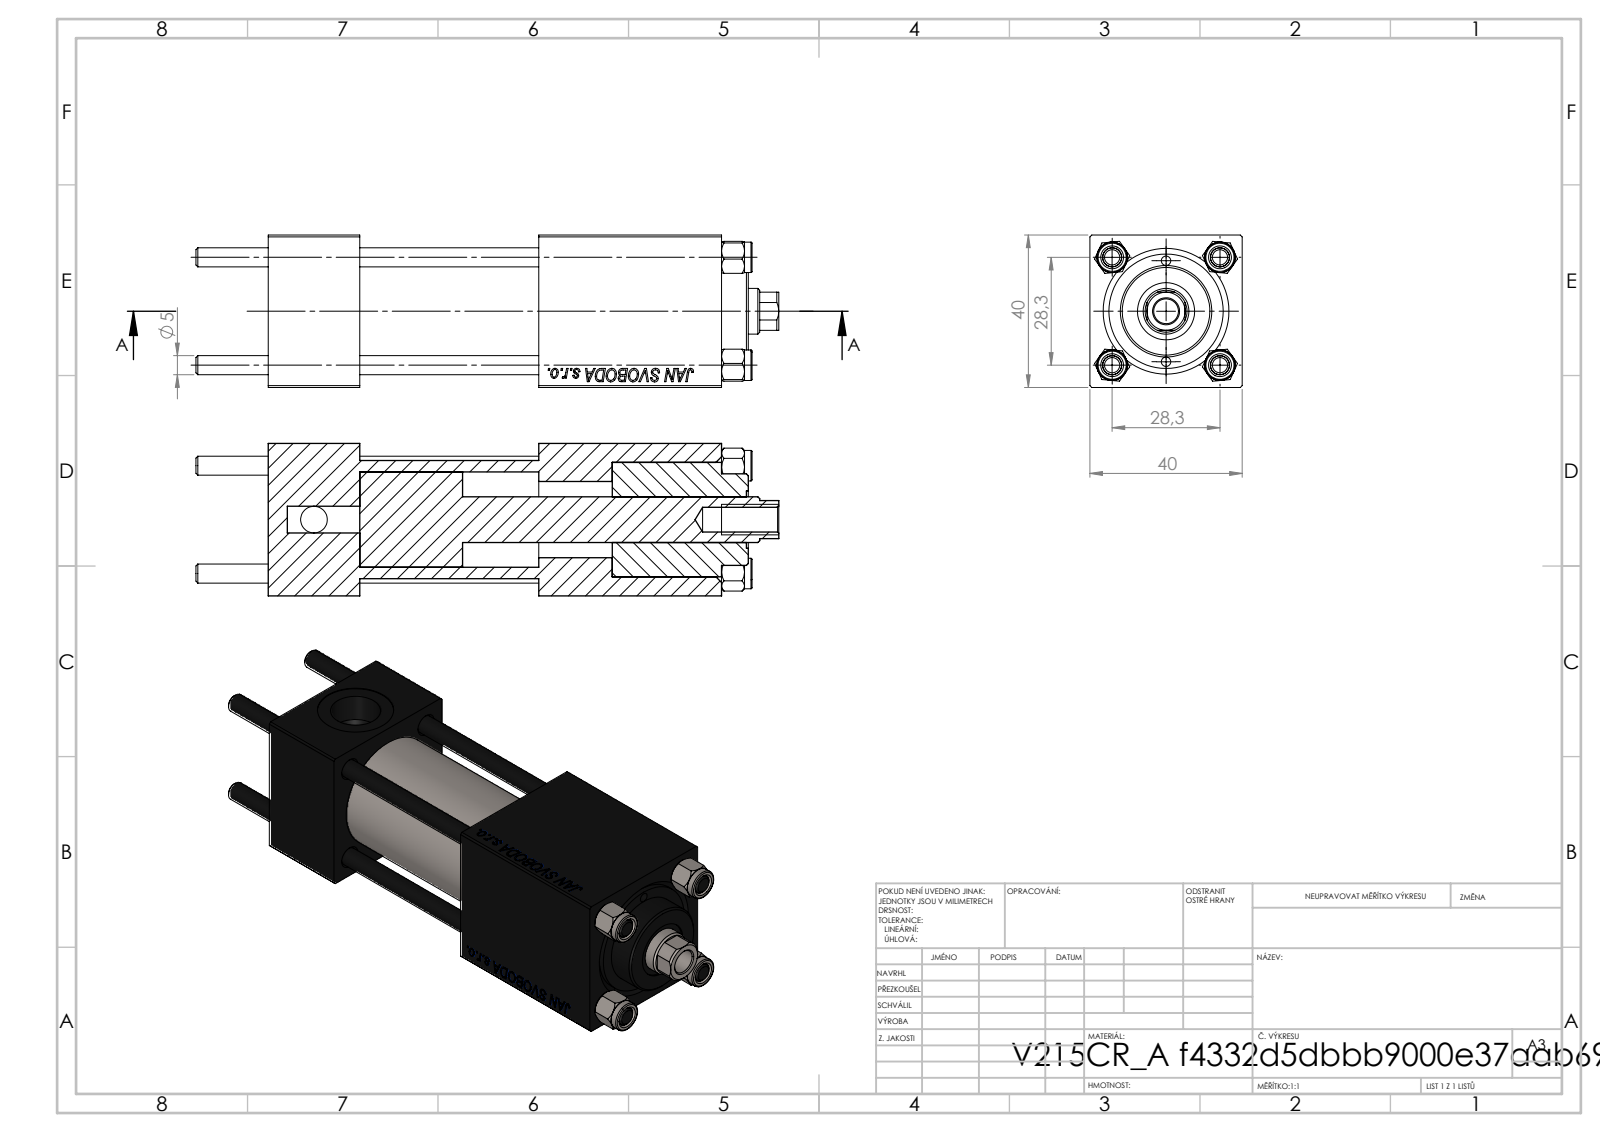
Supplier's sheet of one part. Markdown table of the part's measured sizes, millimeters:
| quantity | value |
| --- | --- |
| part name | V215_VC_A; NUT_M5; V215CR_VCP; V215CR_BODY_A (+1 more) |
| STEP written by | SolidWorks 2019 (CONFIG_CONTROL_DESIGN) |
| units | millimeters |
| bodies | 11 solids, 1137 faces (519 planar, 82 cylindrical, 536 other) |
| overall size | 153 × 40 × 40 |
| volume | 145 026 mm³ |
| surface area | 58 885 mm² |
| round holes (diameter × count) | 5 × 4, 20 × 3, 2.5 × 2, 7 × 2, 13.16 × 2, 6.5 × 1, 12 × 1, 15 × 1, 25 × 1, 30 × 1 |
| round bosses / shafts (diameter × count) | 8 × 4, 31 × 1, 24 × 1 |
| partial cylindrical surfaces (radius × count) | 5.5 × 1 |
| main face-to-face distances | 40, 24, 90.3, 66.3, 119, 95, 28.7, 71, 47, 19.3 |
| hole center spacings | 14.18, 20.01, 28.3, 30.84, 13.25, 40.02, 26.5, 72 |
